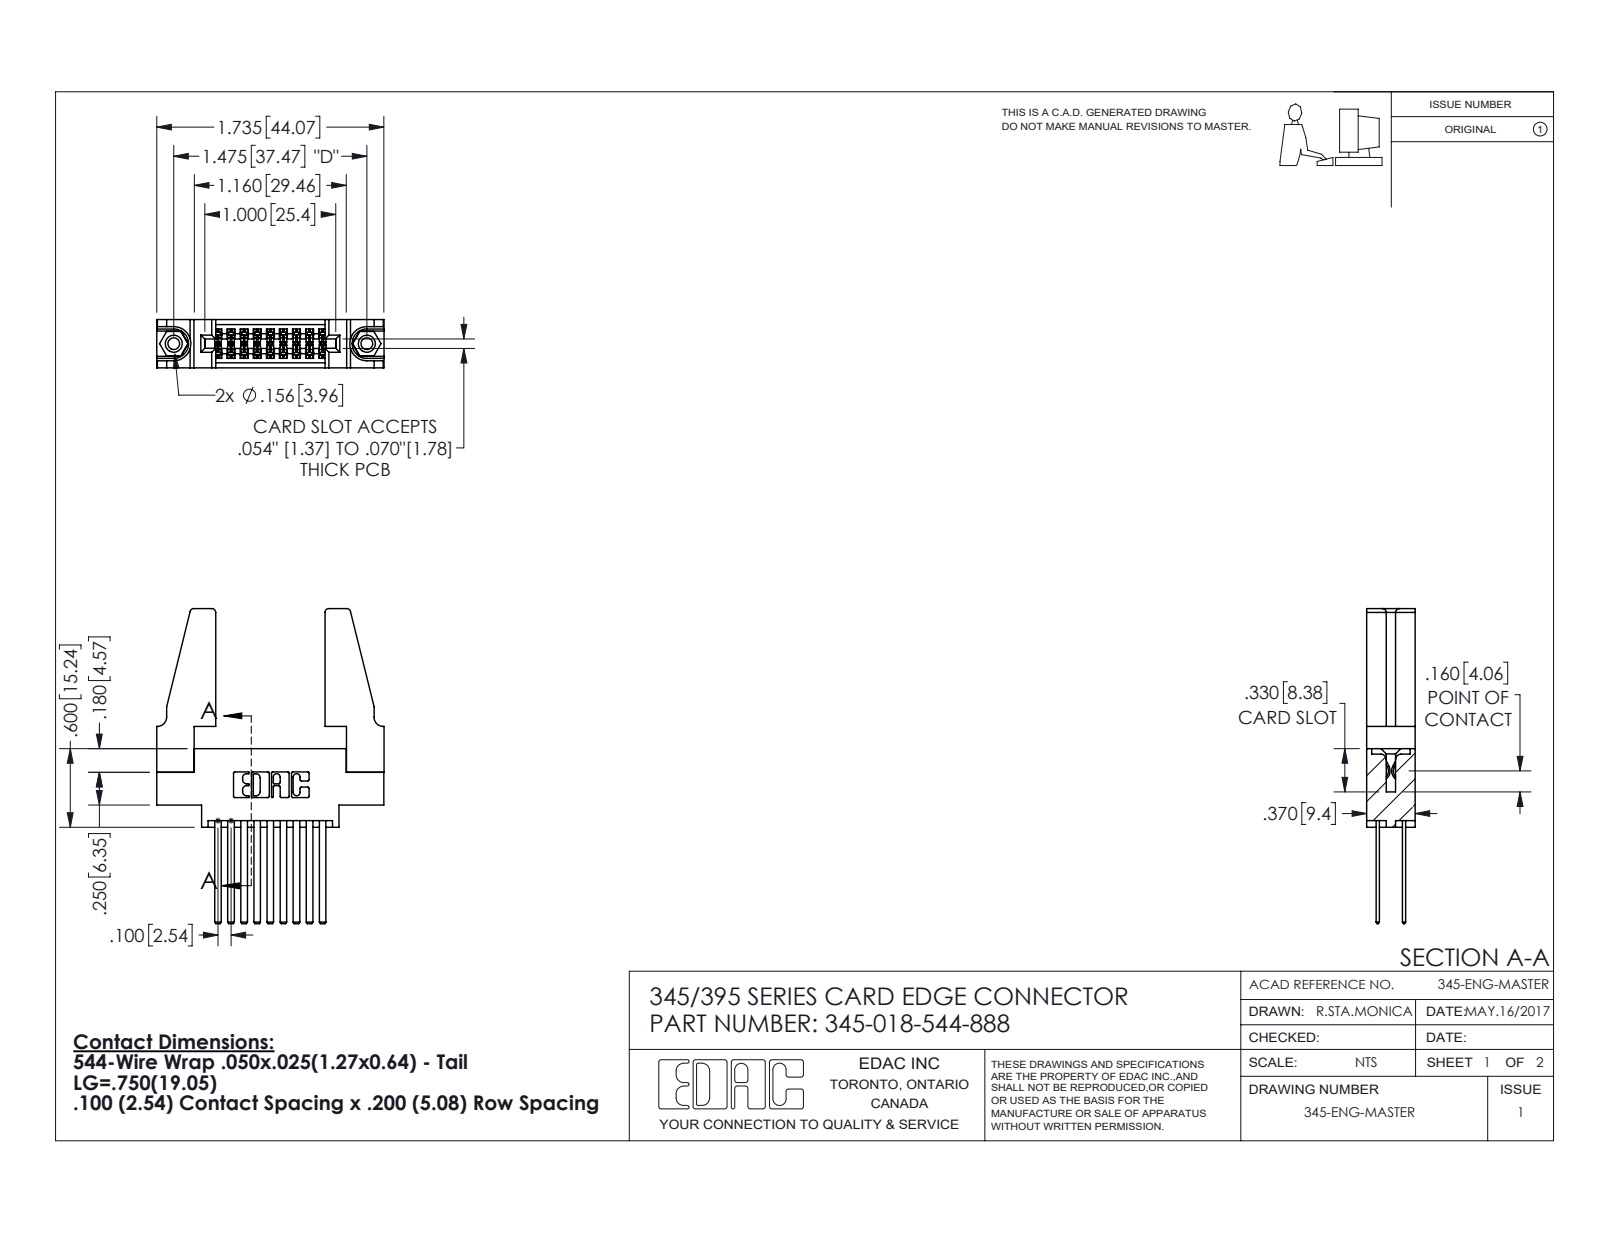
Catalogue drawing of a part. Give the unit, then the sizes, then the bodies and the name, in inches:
Units: inches
Overall size (bounding box): 2.407 × 1.736 × 0.37
Round holes (diameter × count): ⌀0.089 ×2, ⌀0.125 ×2, ⌀0.156 ×2, ⌀0.064 ×1
Round bosses / shafts (diameter × count): ⌀0.155 ×2
Partial cylindrical surfaces — rounded edges, fillets, slot ends (radius × count): R0.006 ×27, R0.01 ×22, R0.03 ×8, R0.007 ×6, R0.031 ×6, R0.026 ×3, R0.014 ×2, R0.019 ×2
Main face-to-face distances: 0.37, 0.072, 0.298, 0.2, 0.098, 0.272, 0.025, 0.225, 0.175, 0.15
Hole centre spacings: 0.27, 1.244, 1.475
Volume: 0.45 in³ · Surface area: 14.65 in²
Bodies: 23 solids, 1046 faces (678 planar, 352 cylindrical, 16 other)
Part name (STEP PRODUCT): 345 Part_0.170 Offset - 0.156 Dia-TH; 345-018-544-888; 345-292-001_345-293-144; 345-220-078_345-220-088 (+1 more)
STEP written by: SolidWorks 2016 (CONFIG_CONTROL_DESIGN)
